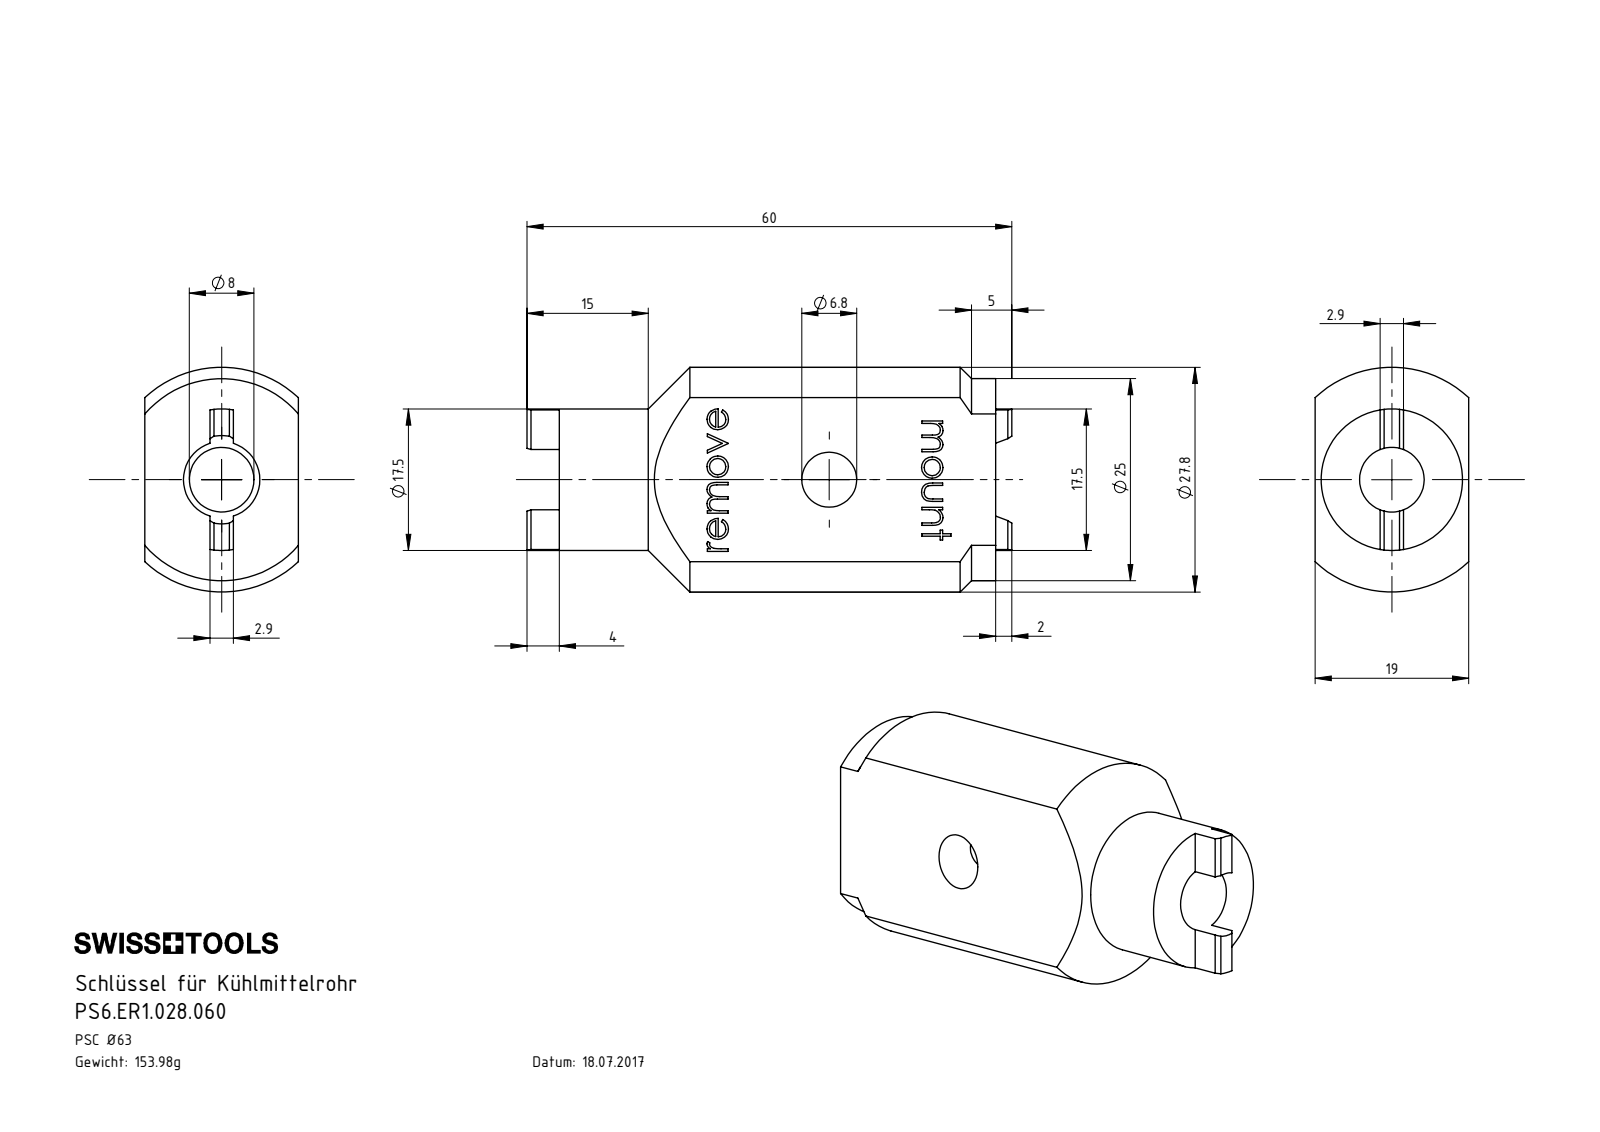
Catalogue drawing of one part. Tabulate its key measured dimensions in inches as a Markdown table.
| quantity | value |
| --- | --- |
| part name | PS6-ER1.028.060_B |
| STEP written by | SolidWorks 2017 (CONFIG_CONTROL_DESIGN) |
| units | inches |
| bodies | 1 solid, 204 faces (107 planar, 14 cylindrical, 83 other) |
| overall size | 2.362 × 1.094 × 0.748 |
| volume | 1.197 in³ |
| surface area | 9.903 in² |
| round holes (diameter × count) | 0.268 × 1, 0.315 × 1 |
| round bosses / shafts (diameter × count) | 0.689 × 1 |
| partial cylindrical surfaces (radius × count) | 0.492 × 1, 0.547 × 1 |
| main face-to-face distances | 0.748, 2.126, 0.317, 0.431, 0.114, 0.313, 0.427, 0.744, 0.157, 2.283 |
